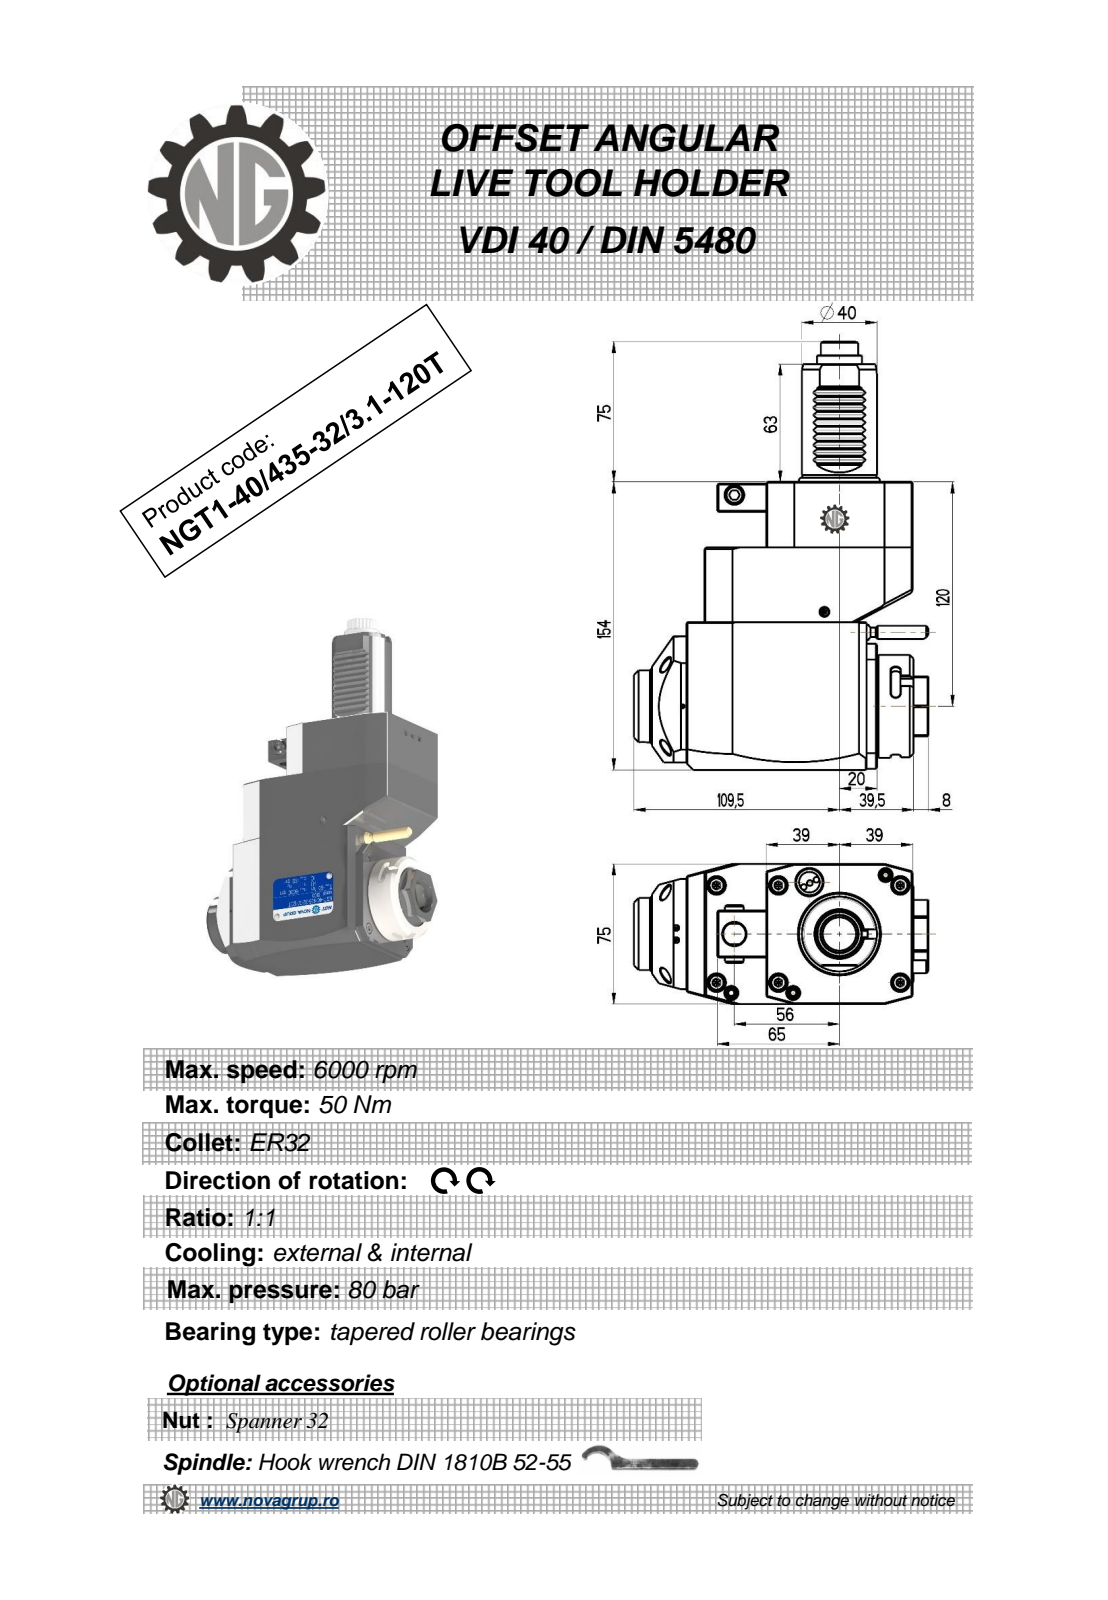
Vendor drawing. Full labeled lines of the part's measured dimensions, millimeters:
Part name (STEP PRODUCT): NGT1_40_435_32_3_1_120T
STEP written by: PRO/ENGINEER BY PARAMETRIC TECHNOLOGY CORPORATION, 2010280 (CONFIG_CONTROL_DESIGN)
Units: millimetres
Bodies: 1 solid, 453 faces (195 planar, 162 cylindrical, 96 other)
Overall size (bounding box): 229 × 157 × 75
Volume: 1 287 000 mm³ · Surface area: 90 358 mm²
Round holes (diameter × count): ⌀2.5 ×1, ⌀3 ×1, ⌀8.5 ×1, ⌀9.5 ×1, ⌀12 ×1, ⌀23 ×1
Round bosses / shafts (diameter × count): ⌀8.96 ×2, ⌀55 ×1, ⌀48 ×1, ⌀40 ×1, ⌀38.5 ×1, ⌀24 ×1, ⌀10 ×1, ⌀7 ×1
Partial cylindrical surfaces — rounded edges, fillets, slot ends (radius × count): R2.08 ×48, R0.3 ×10, R2.5 ×6, R180 ×2, R9.08 ×1, R9.92 ×1, R15 ×1, R24.5 ×1
Main face-to-face distances: 75, 154, 19, 111, 35, 59, 92, 119, 0.5, 33
Hole centre spacings: 43.2, 74.1, 111.5
